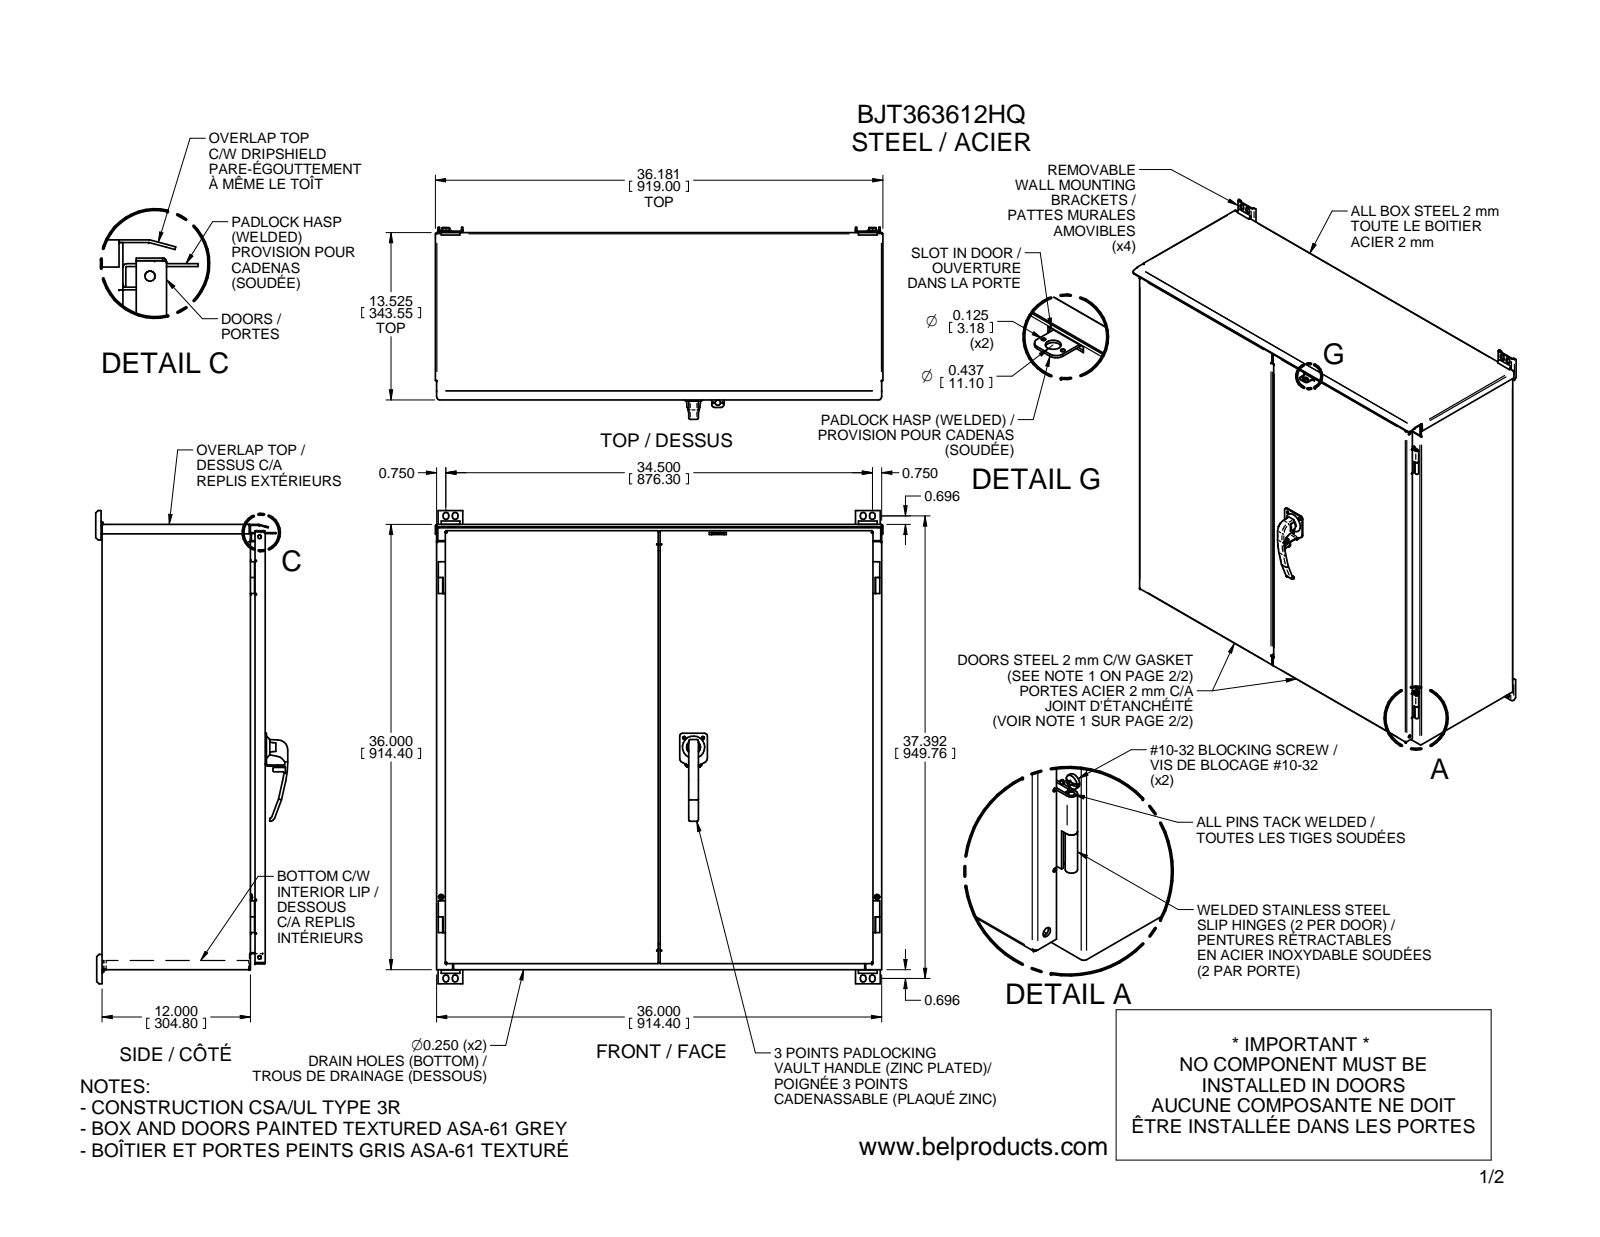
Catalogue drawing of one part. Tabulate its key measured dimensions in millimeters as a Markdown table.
| quantity | value |
| --- | --- |
| part name | BJT363612HQ-A8F3; BJT363612HQ_BOITIER; BJT363612HQ-B; BJT363612HQ-EB (+8 more) |
| STEP written by | ST-DEVELOPER v16.7 (AUTOMOTIVE_DESIGN) |
| units | millimeters |
| bodies | 54 solids, 1207 faces (752 planar, 341 cylindrical, 114 other) |
| overall size | 971.96 × 919 × 394.67 |
| volume | 6 685 000 mm³ |
| surface area | 6 785 000 mm² |
| round holes (diameter × count) | 3.16 × 16, 7.92 × 8, 11.58 × 8, 5.11 × 7, 3.17 × 6, 12.7 × 6, 7.14 × 4, 9.02 × 4, 9.53 × 4, 10.31 × 4, 10.54 × 4, 6.38 × 3 |
| round bosses / shafts (diameter × count) | 3.17 × 16, 20.62 × 4, 3.02 × 4, 25.12 × 2, 10.87 × 2, 8.56 × 2, 7.8 × 2, 6.35 × 2 |
| partial cylindrical surfaces (radius × count) | 0.81 × 42, 2.72 × 34, 5.79 × 16, 1.59 × 15, 3.17 × 12, 2.1 × 8, 2.34 × 8, 4.76 × 8 |
| main face-to-face distances | 1.91, 333.32, 1.9, 331.41, 912.5, 335.23, 914.4, 910.59, 910.6, 912.49 |
| hole center spacings | 68.66, 696.52, 876.3, 19.05, 49.84, 68.65, 118.14, 124.23 |
